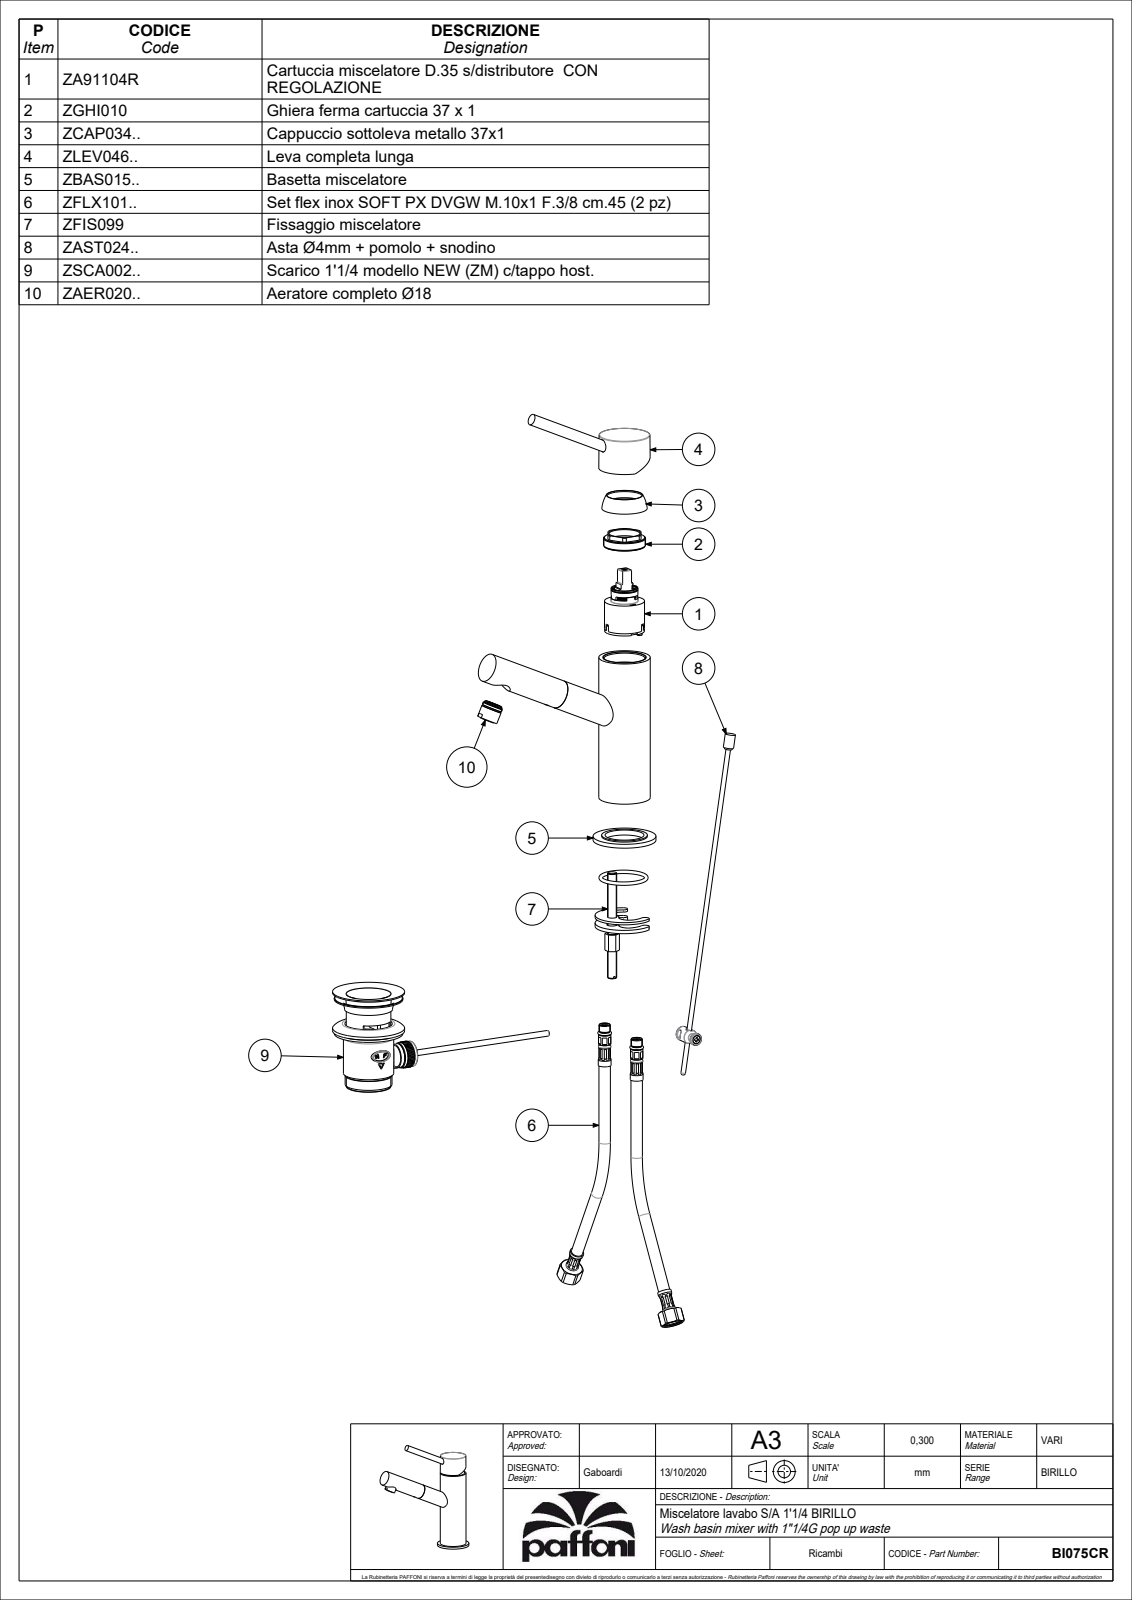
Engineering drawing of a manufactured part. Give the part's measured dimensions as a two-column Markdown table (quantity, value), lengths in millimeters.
| quantity | value |
| --- | --- |
| part name | BI075CR |
| STEP written by | CREO PARAMETRIC BY PTC INC, 2020044 (CONFIG_CONTROL_DESIGN) |
| units | millimeters |
| bodies | 4 solids, 1290 faces (673 planar, 336 cylindrical, 281 other) |
| overall size | 192.84 × 178.35 × 55 |
| volume | 257 077 mm³ |
| surface area | 80 550 mm² |
| round holes (diameter × count) | 4.5 × 4, 11 × 3, 4 × 2, 5 × 2, 6.5 × 2, 9 × 2, 3.3 × 1, 5.5 × 1, 7.25 × 1, 10 × 1, 15.5 × 1, 18.4 × 1 |
| round bosses / shafts (diameter × count) | 11.2 × 2, 10.8 × 2, 10 × 2, 8.2 × 2, 55 × 1, 45 × 1, 40 × 1, 35 × 1 |
| partial cylindrical surfaces (radius × count) | 0.5 × 51, 1.26 × 14, 2.05 × 14, 0.15 × 11, 0.3 × 4, 1 × 2, 1.05 × 1, 3 × 1 |
| main face-to-face distances | 26.5, 132.1, 3.5, 4.5, 5.5, 23, 121.5, 104.3, 100.8, 77.8 |
| hole center spacings | 3.54, 8.06, 8.75, 10.97, 14.01, 15.89, 12.5, 15 |
